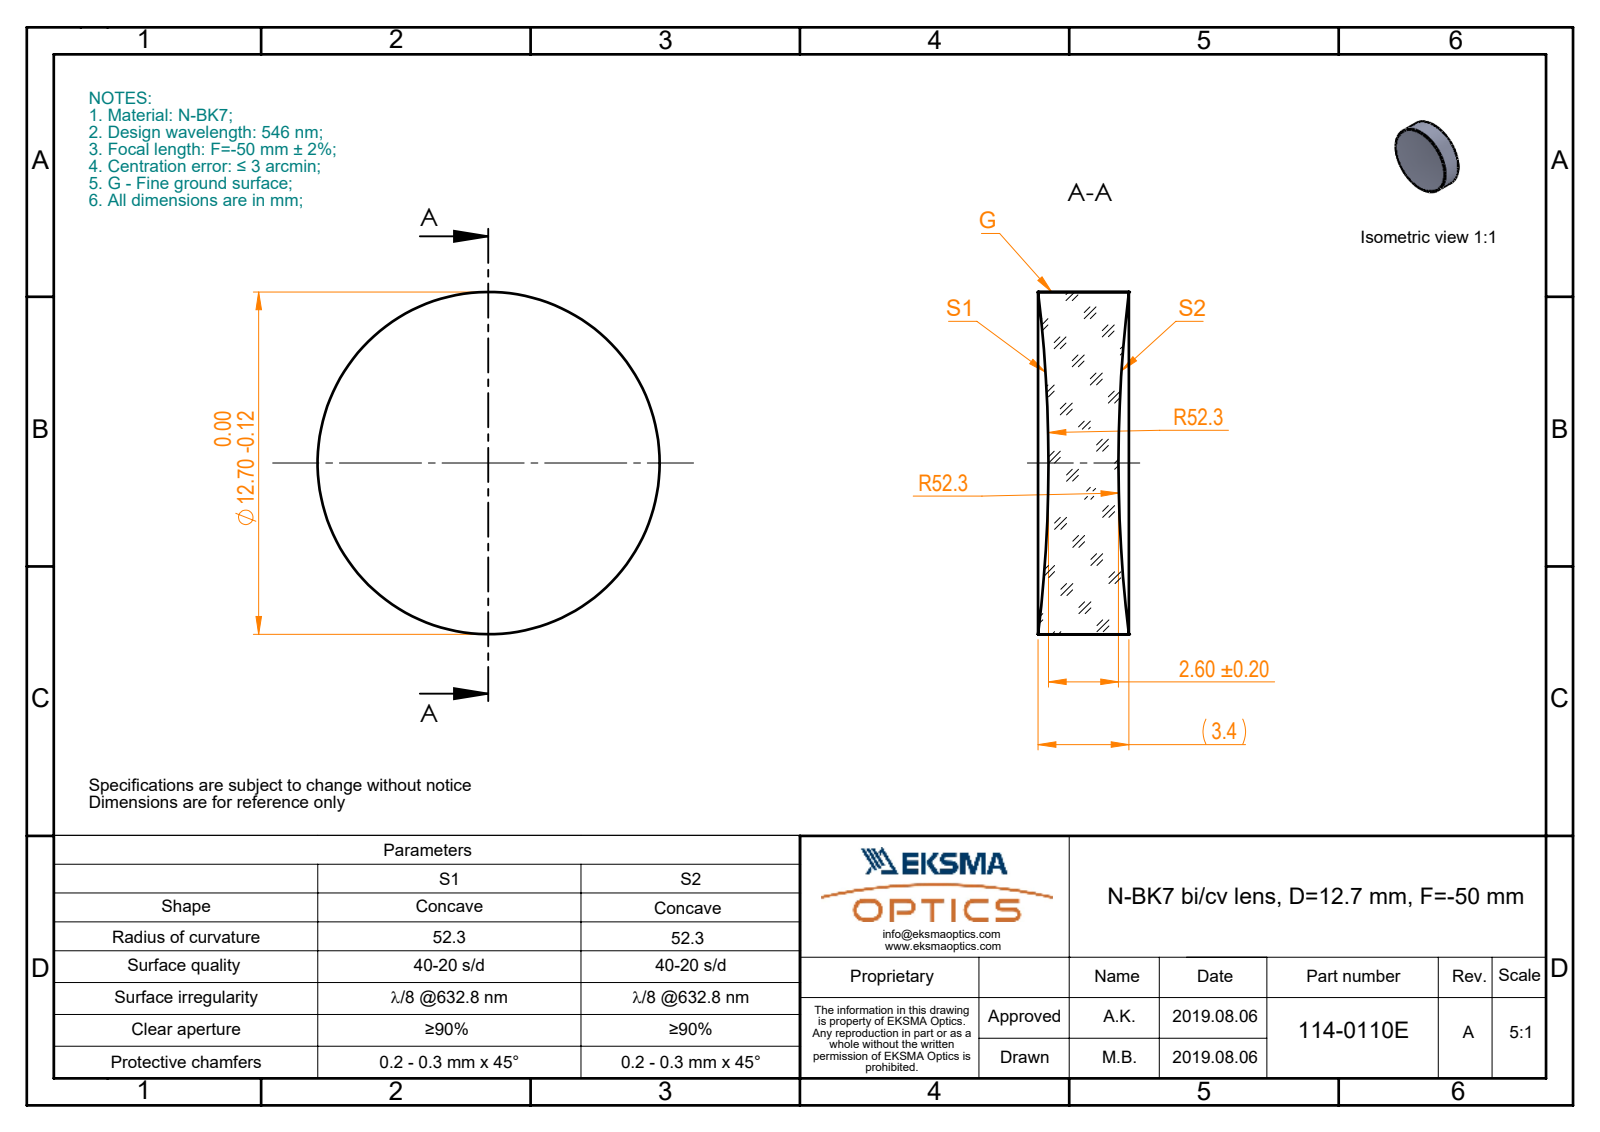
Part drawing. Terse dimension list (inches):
name: 114-0110E BK7 bi-cv 12.7 F-50
written by: SolidWorks 2017 (CONFIG_CONTROL_DESIGN)
unit: in
bodies: 1 solid, 6 faces (0 planar, 2 cylindrical, 4 other)
size: 0.5 × 0.5 × 0.133
volume: 0.023 in³; area: 0.603 in²
bosses: 1× ⌀0.5
